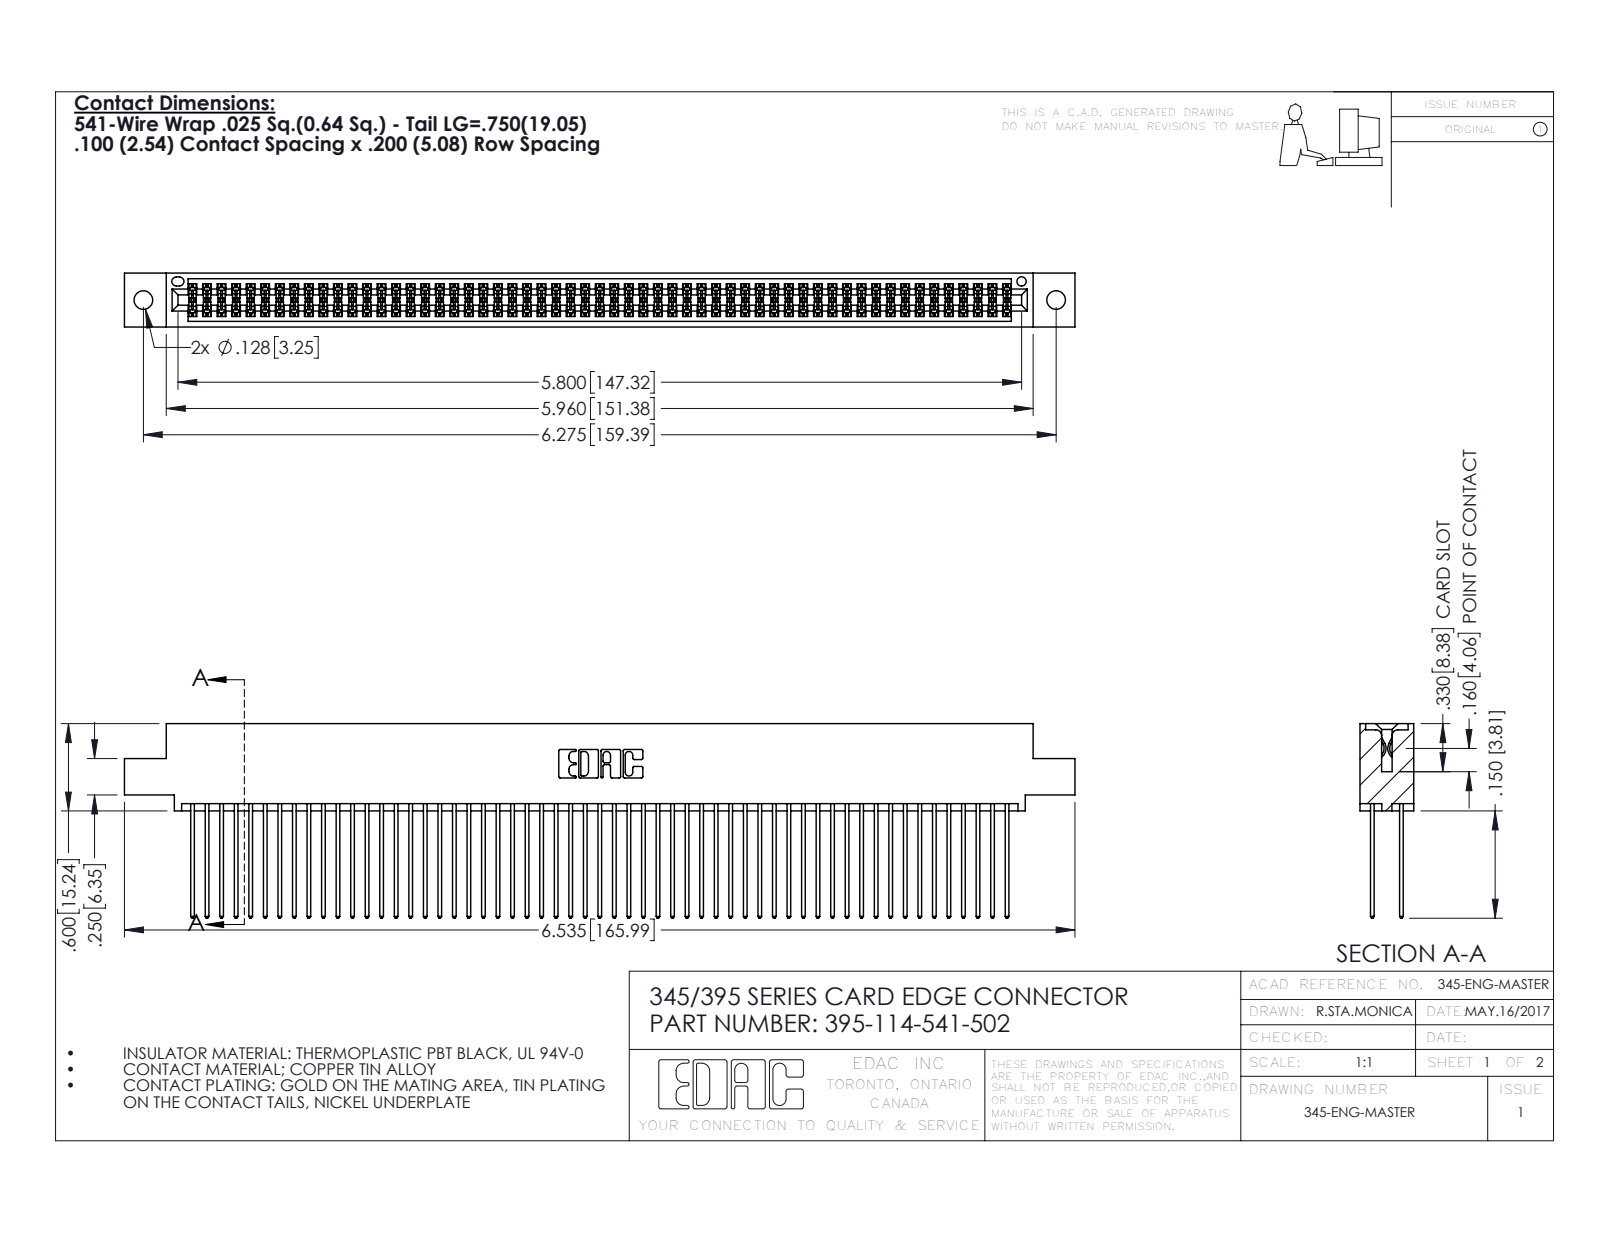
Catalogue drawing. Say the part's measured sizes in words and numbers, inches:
The part is named "345 Part_0.110 Offset - 0.128 Dia; 395-114-541-502; 345-292-001_345-293-141". Its 3-D file was written by "SolidWorks 2016 (CONFIG_CONTROL_DESIGN)". It is 115 solids with 5830 faces: 3846 planar, 1984 cylindrical and 0 other. Overall it measures 6.535 by 1.337 by 0.37 inches. Its volume is 1.026 cubic inches and its surface area 43.45 square inches. Round holes: 2 of diameter 0.128, 1 of diameter 0.064. Partial cylindrical surfaces (rounded edges, fillets, slot ends): 171 of radius 0.006, 114 of radius 0.01, 22 of radius 0.01, 6 of radius 0.007, 6 of radius 0.031, 3 of radius 0.026, 2 of radius 0.014, 2 of radius 0.019. The main face-to-face distances are 0.072, 0.298, 0.2, 0.098, 0.272, 0.025, 0.225, 0.37, 0.175, 0.149. The hole center spacings are 0.27, 6.039, 6.275.
